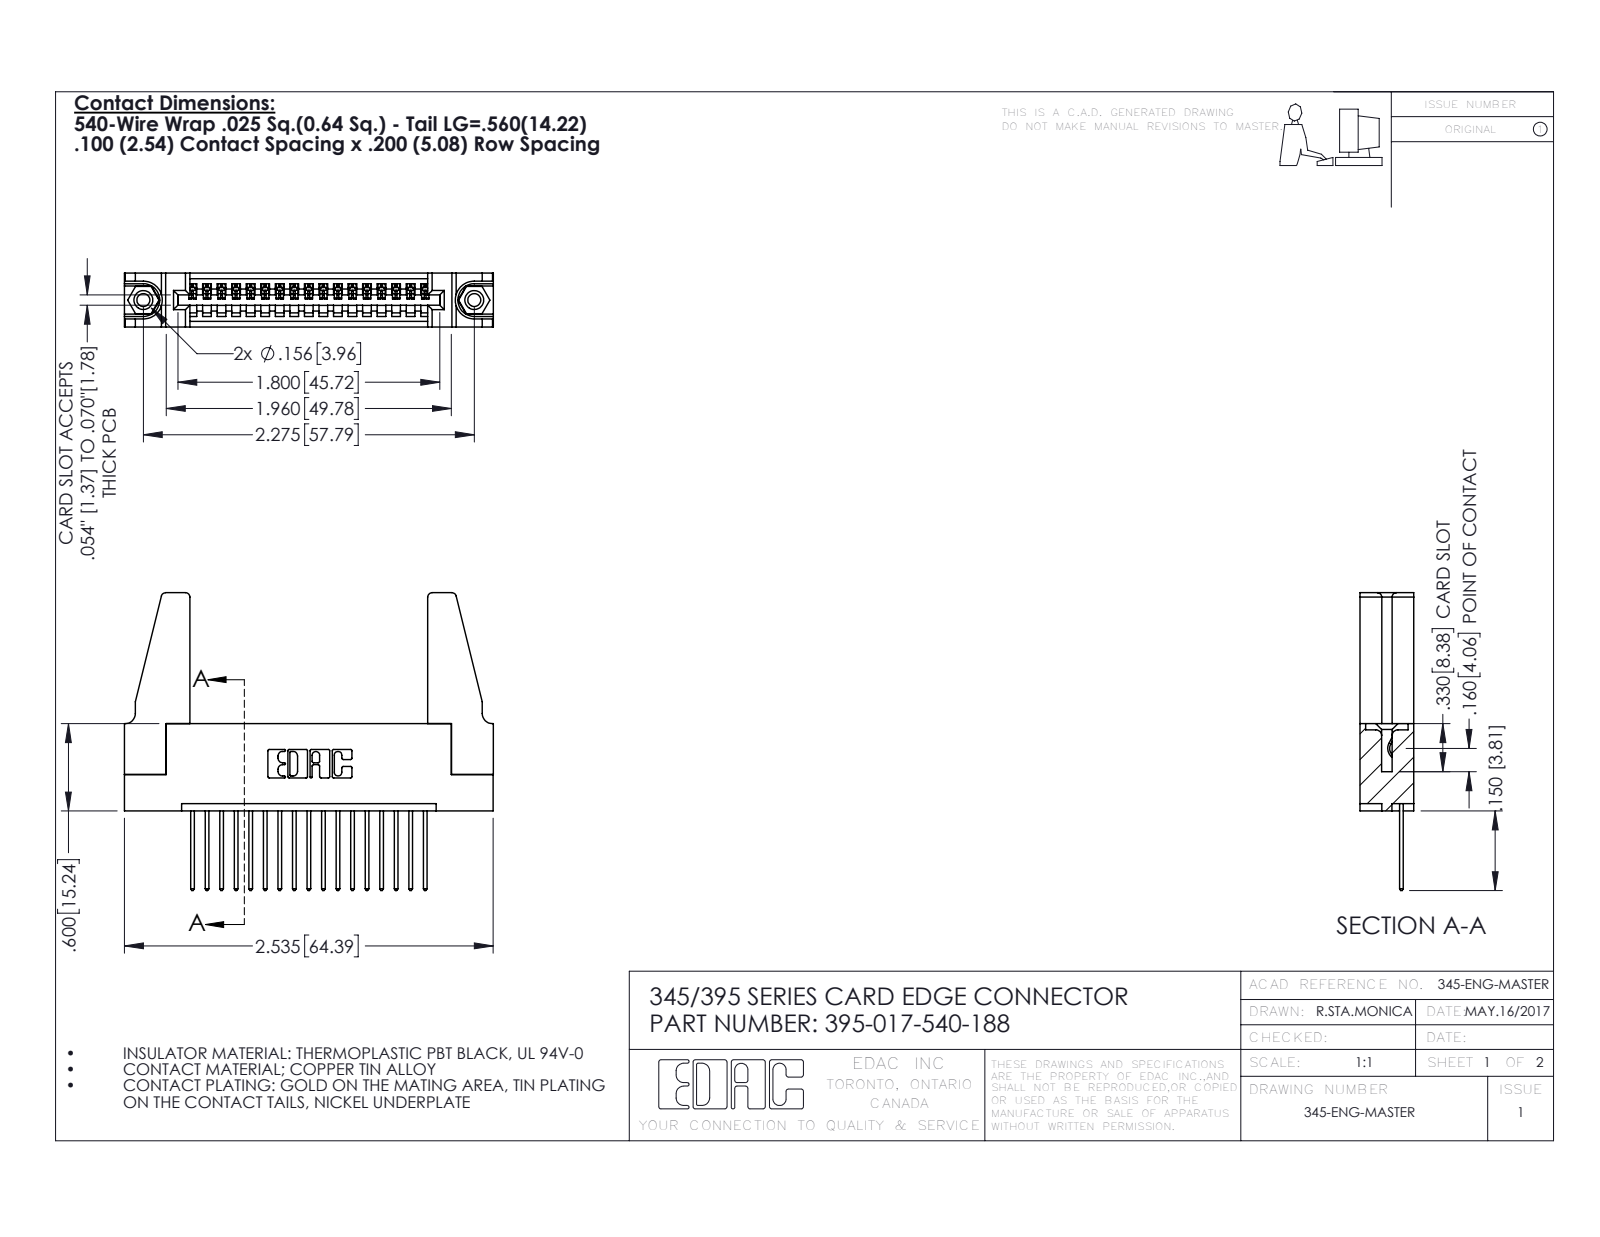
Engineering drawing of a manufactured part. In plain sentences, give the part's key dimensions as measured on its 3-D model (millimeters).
The part is named "345-292-001_345-293-140; 345 Part_Flush Mounting Lugs - 0.156 Dia-TH; 345-220-078_345-220-088; 345-250-001_345-250-001-102 (+1 more)". Its 3-D file was written by "SolidWorks 2016 (CONFIG_CONTROL_DESIGN)". It is 22 solids with 1236 faces: 832 planar, 388 cylindrical and 16 other. Overall it measures 64.4 by 52 by 9.4 millimeters. Its volume is 9 190 cubic millimeters and its surface area 10 850 square millimeters. Round holes: 2 of diameter 2.3, 2 of diameter 3.2, 2 of diameter 4, 1 of diameter 1.6. Round bosses or shafts: 2 of diameter 3.9. Partial cylindrical surfaces (rounded edges, fillets, slot ends): 34 of radius 0.2, 34 of radius 0.3, 22 of radius 0.3, 8 of radius 0.8, 6 of radius 0.2, 6 of radius 0.8, 3 of radius 0.7, 2 of radius 0.8. The main face-to-face distances are 9.4, 1.8, 7.6, 5.1, 2.5, 6.9, 0.6, 5.7, 3.8, 3.8. The hole center spacings are 6.9, 51.8, 57.8.
